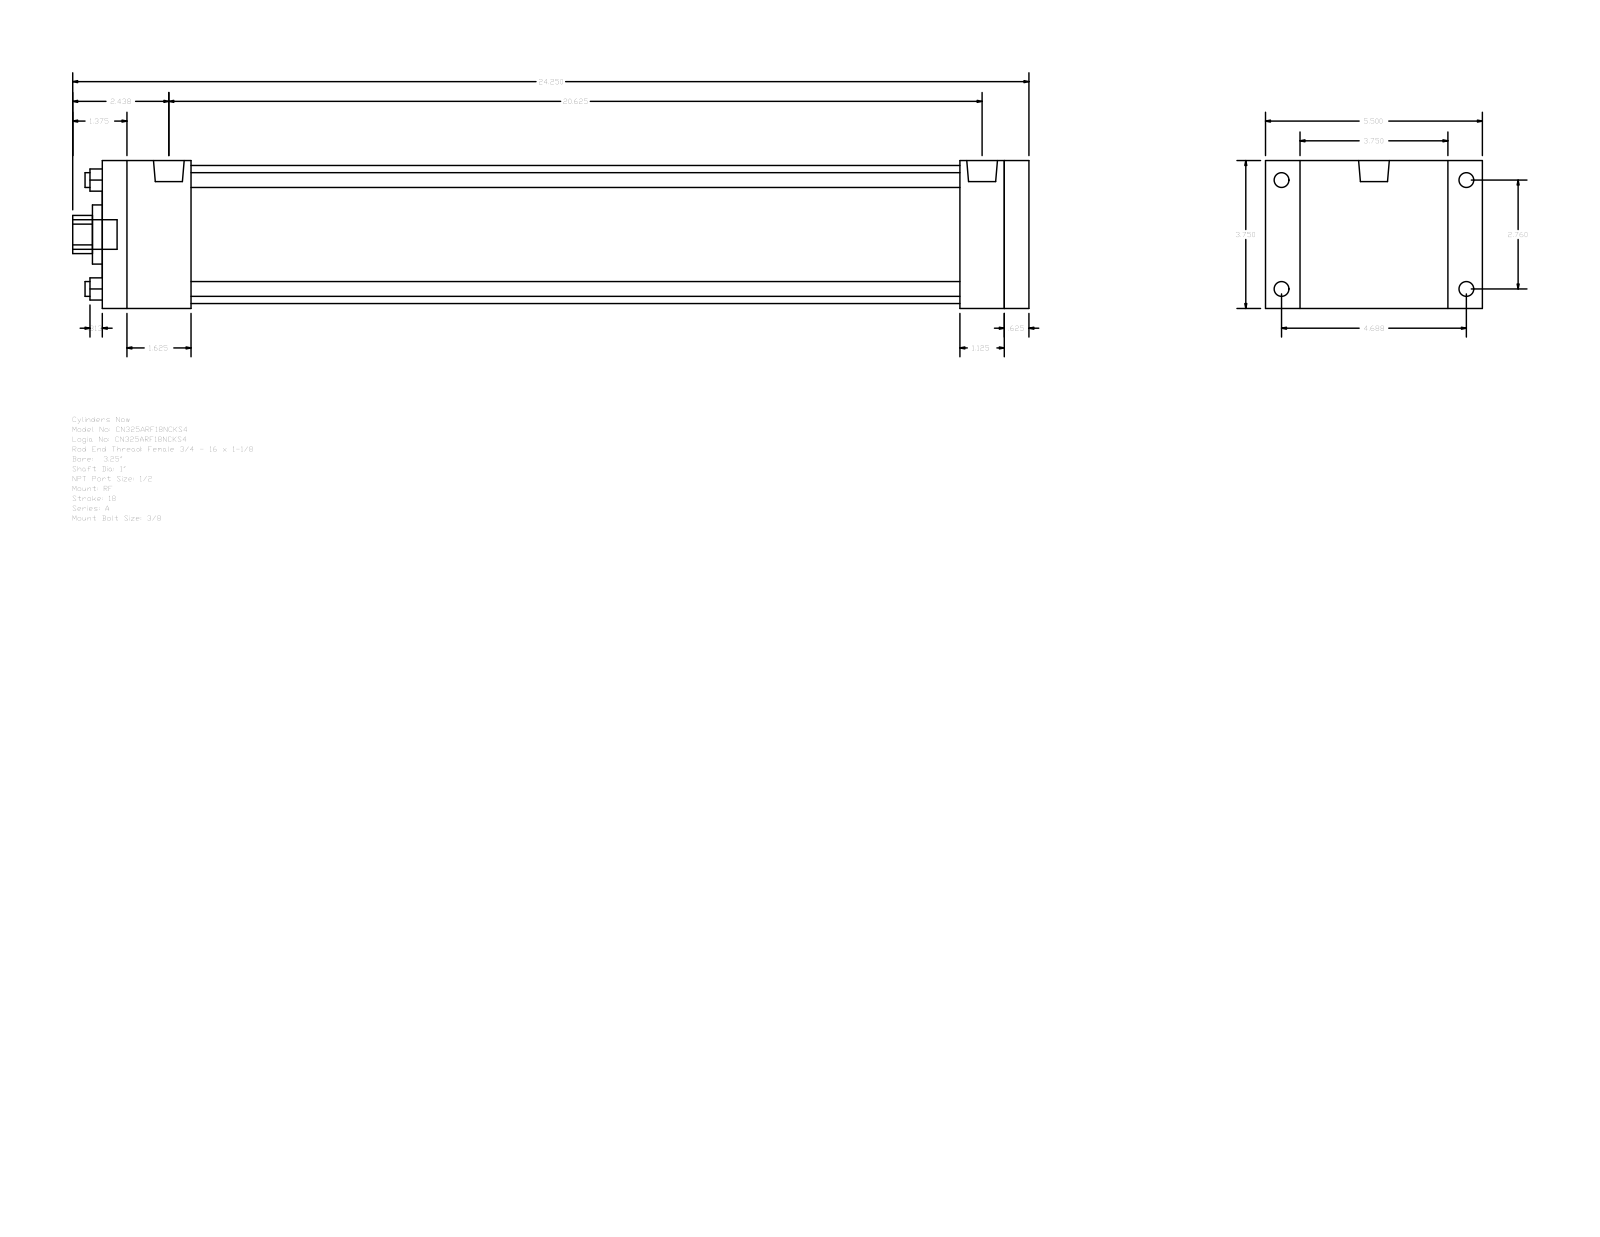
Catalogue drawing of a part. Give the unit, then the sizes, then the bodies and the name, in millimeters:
Units: millimetres
Overall size (bounding box): 615.95 × 139.7 × 95.25
Round holes (diameter × count): ⌀9.53 ×4, ⌀25.4 ×1, ⌀38.1 ×1, ⌀88.9 ×1
Round bosses / shafts (diameter × count): ⌀9.53 ×4, ⌀8.73 ×4, ⌀19.77 ×2, ⌀19.05 ×1
Partial cylindrical surfaces — rounded edges, fillets, slot ends (radius × count): R12.29 ×1
Main face-to-face distances: 95.24, 596.9, 15.87, 581.03, 22.23, 117.47, 552.45, 28.58, 44.45, 57.15
Hole centre spacings: 49.57, 70.1, 99.14
Bodies: 0 solids, 92 faces (64 planar, 28 cylindrical, 0 other)
Part name (STEP PRODUCT): A_RF__0325_1
STEP written by: GSSL Pune (CONFIG_CONTROL_DESIGN)
